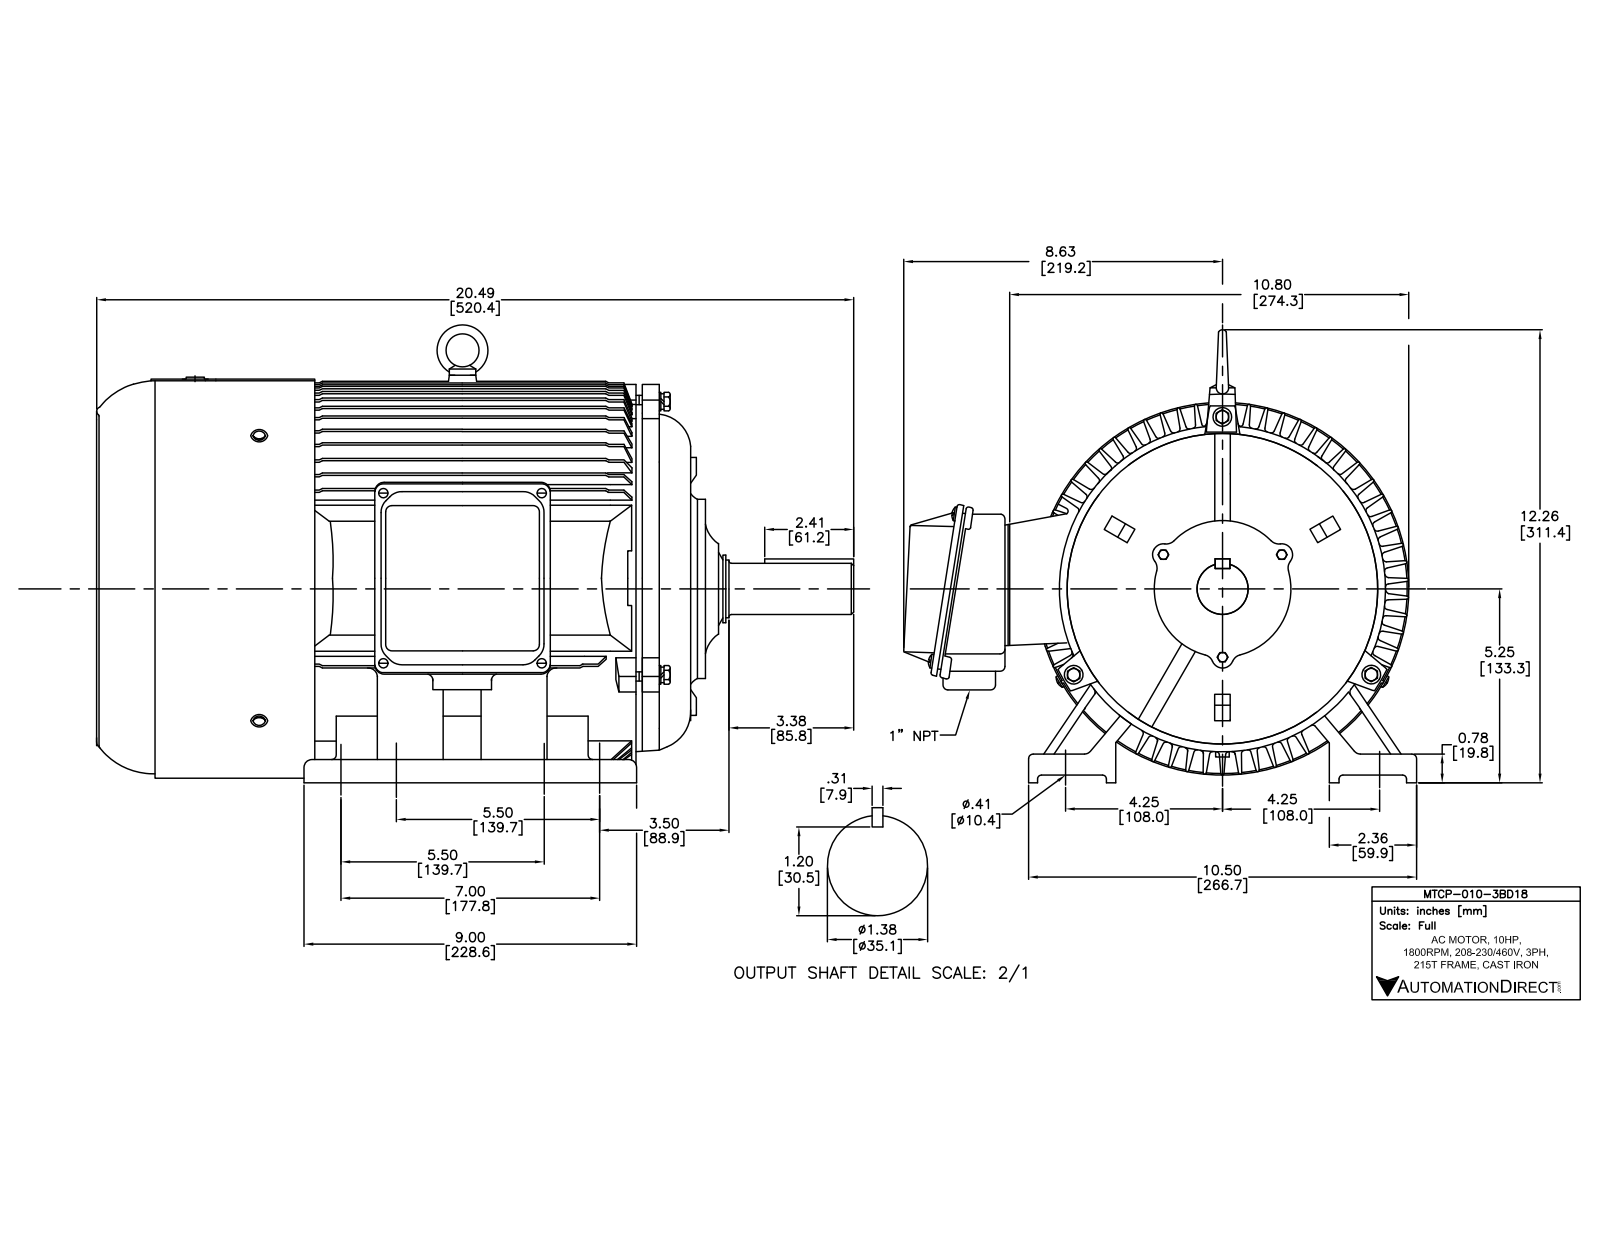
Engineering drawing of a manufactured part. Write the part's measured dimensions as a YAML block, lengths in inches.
part_name: "hex head bolts-full thread grade c gb_GB_FASTENER_BOLT_HHBFTC M5X10-N; hex head bolts-full thread grade c gb_GB_FASTENER_BOLT_HHBFTC M8X40-N; hex head bolts-full thread grade c gb_GB_FASTENER_BOLT_HHBFTC M5X16-N; spring lock washers--normal type gb_GB_FASTENER_WASHER_SW 5 (+6 more)"
step_written_by: "SolidWorks 2017 (AUTOMOTIVE_DESIGN)"
units: inches
bodies: {solids: 48, faces: 2925, planar: 770, cylindrical: 1091, other: 1064}
overall_size: [20.427, 14.291, 12.892]
volume: 257
surface_area: 2593
round_holes:
  - {diameter: 0.228, count: 14}
  - {diameter: 0.165, count: 11}
  - {diameter: 0.354, count: 8}
  - {diameter: 0.079, count: 4}
  - {diameter: 0.197, count: 3}
  - {diameter: 0.209, count: 3}
  - {diameter: 0.213, count: 3}
  - {diameter: 0.331, count: 3}
  - {diameter: 0.342, count: 3}
  - {diameter: 0.394, count: 3}
  - {diameter: 0.268, count: 1}
  - {diameter: 0.315, count: 1}
round_bosses_or_shafts:
  - {diameter: 0.197, count: 8}
  - {diameter: 0.315, count: 6}
  - {diameter: 0.394, count: 4}
  - {diameter: 0.63, count: 3}
  - {diameter: 0.507, count: 3}
  - {diameter: 11.354, count: 1}
  - {diameter: 10, count: 1}
  - {diameter: 5.118, count: 1}
partial_cylinders:
  - {radius: 0.039, count: 271}
  - {radius: 0.02, count: 67}
  - {radius: 0.118, count: 66}
  - {radius: 0.049, count: 39}
  - {radius: 0.276, count: 28}
  - {radius: 0.079, count: 16}
  - {radius: 0.315, count: 11}
  - {radius: 0.098, count: 10}
face_to_face_distances: [0.197, 0.047, 13.543, 0.236, 0.118, 2.939, 2.986, 16.529, 16.482, 3.222]
hole_center_spacings: [2.677, 3.786, 2.678, 3.937, 1, 4.933, 5.508, 6.008]
